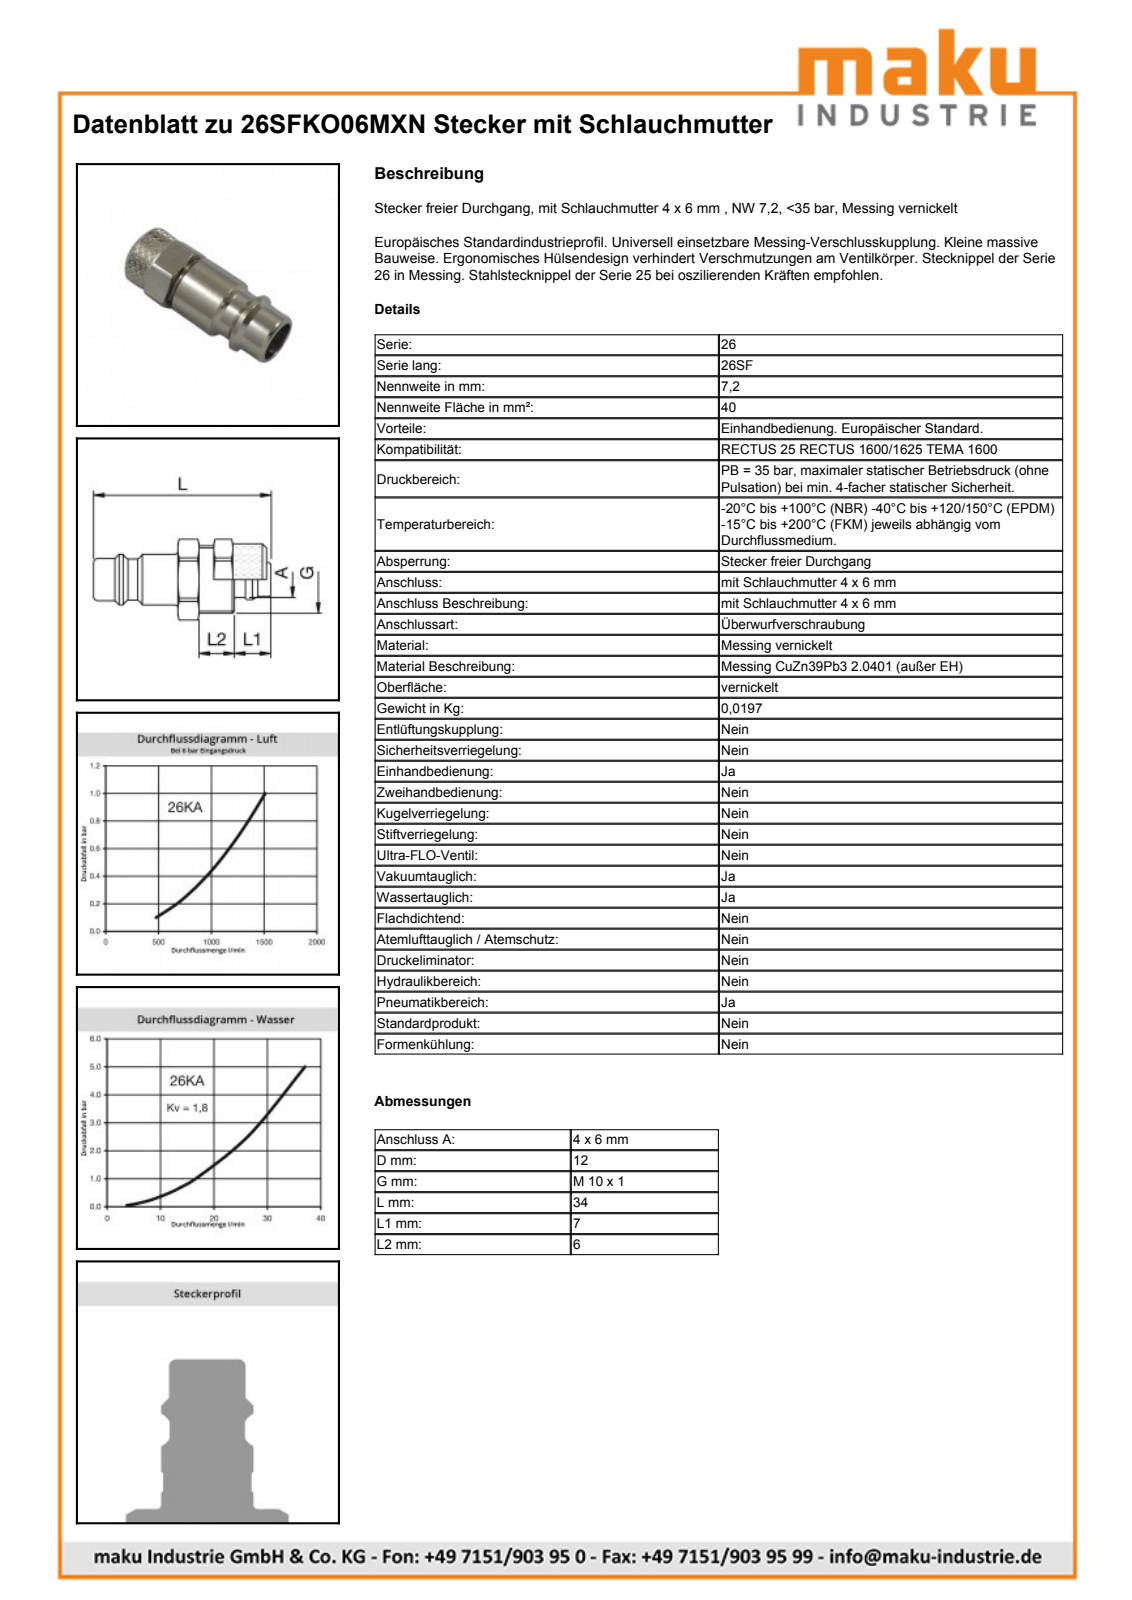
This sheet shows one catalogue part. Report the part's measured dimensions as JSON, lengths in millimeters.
{"part_name": "D102974; D102973; D102670", "step_written_by": "Autodesk Inventor 2011 (AUTOMOTIVE_DESIGN)", "units": "millimeters", "bodies": {"solids": 2, "faces": 60, "planar": 13, "cylindrical": 19, "other": 28}, "overall_size": [34, 13.49, 12.44], "volume_mm3": 2253, "surface_area_mm2": 2637, "round_holes": [[2.95, 1], [6.2, 1], [7.85, 1], [8.92, 1]], "round_bosses_or_shafts": [[12, 1], [10, 1], [9.75, 1], [8.6, 1], [4.6, 1], [3.95, 1]], "partial_cylinders_radius": [[6.75, 1]], "face_to_face_distances": [12, 6.01, 11, 4.99, 12.01, 6, 1.01, 1.09, 7.1, 12.09]}
